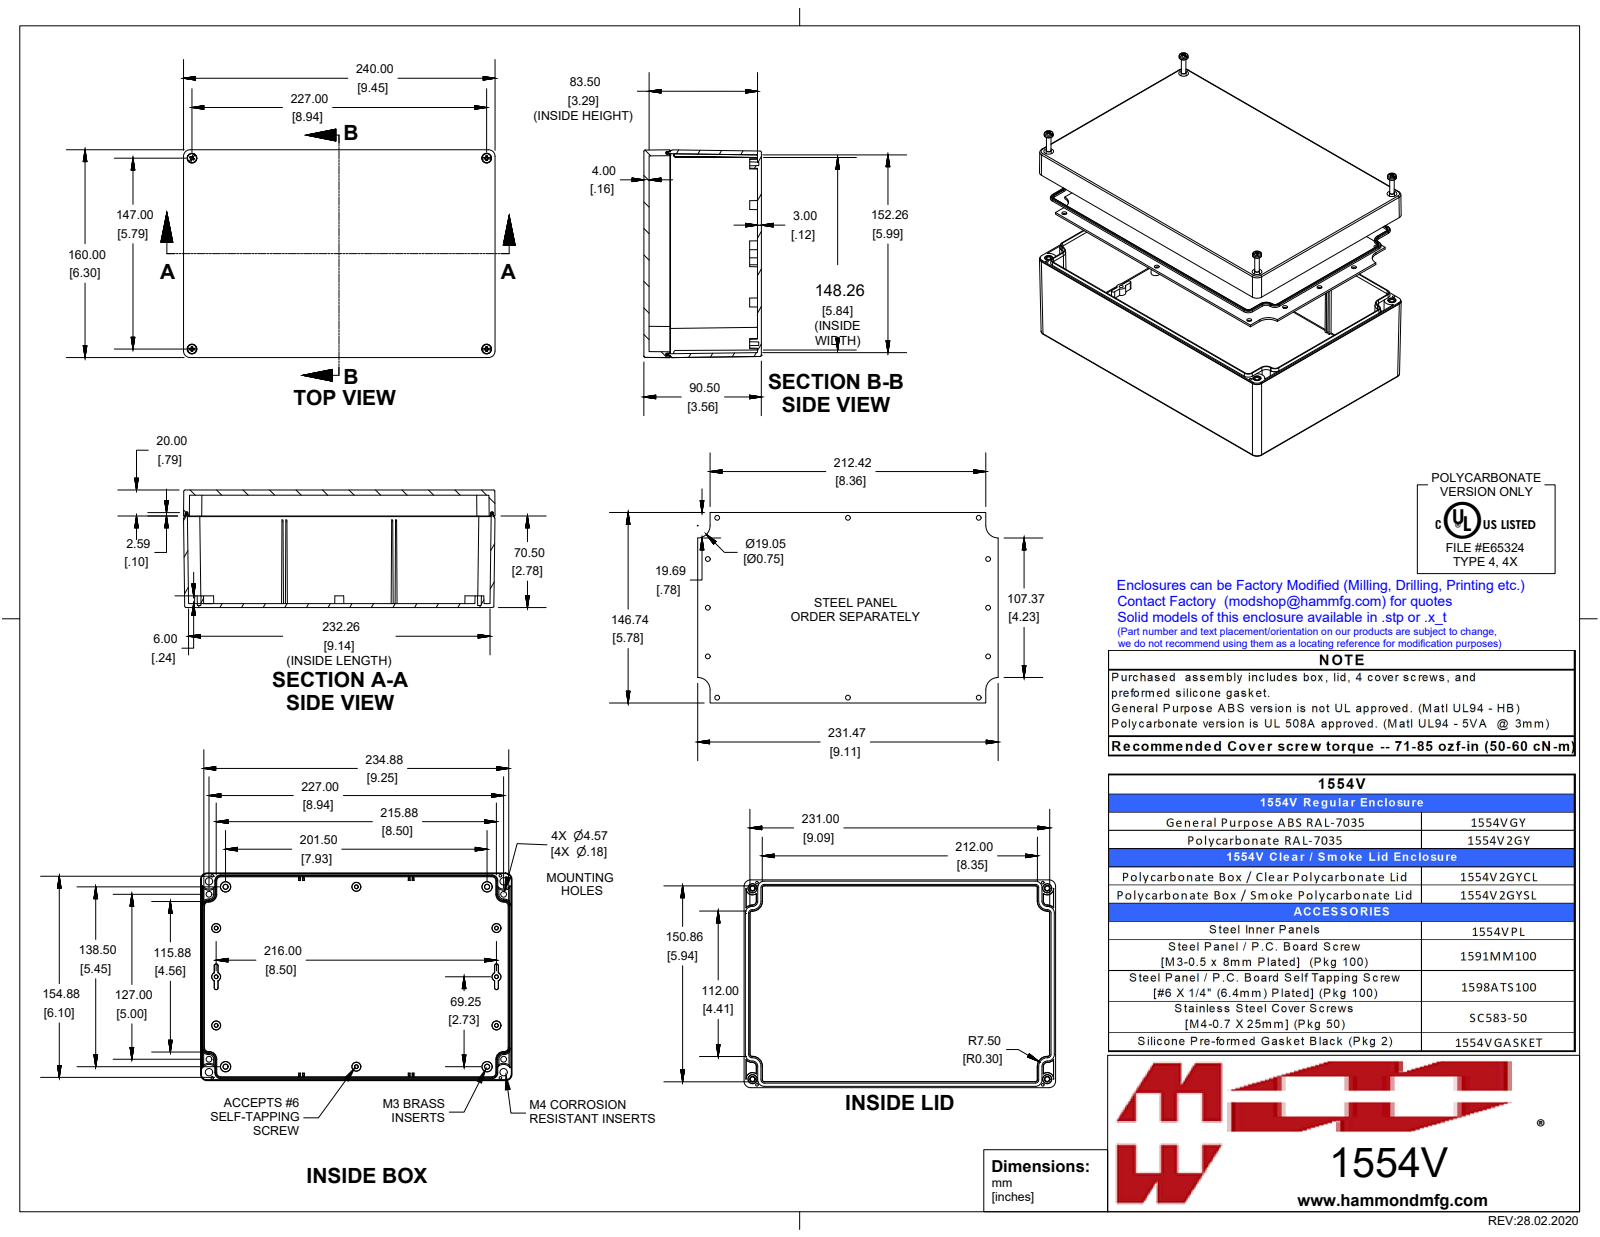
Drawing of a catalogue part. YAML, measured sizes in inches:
part_name: "1554V2GY"
step_written_by: "SolidWorks 2019 (AUTOMOTIVE_DESIGN)"
units: inches
bodies: {solids: 15, faces: 1354, planar: 402, cylindrical: 318, other: 634}
overall_size: [9.449, 6.299, 3.543]
volume: 30.91
surface_area: 503.1
round_holes:
  - {diameter: 0.079, count: 8}
  - {diameter: 0.097, count: 4}
  - {diameter: 0.128, count: 4}
  - {diameter: 0.138, count: 4}
round_bosses_or_shafts:
  - {diameter: 0.272, count: 4}
  - {diameter: 0.25, count: 4}
  - {diameter: 0.218, count: 4}
  - {diameter: 0.21, count: 4}
  - {diameter: 0.19, count: 4}
  - {diameter: 0.154, count: 4}
  - {diameter: 0.152, count: 4}
  - {diameter: 0.15, count: 4}
partial_cylinders:
  - {radius: 0.02, count: 32}
  - {radius: 0.039, count: 8}
  - {radius: 0.197, count: 8}
  - {radius: 0.059, count: 2}
face_to_face_distances: [0.118, 3.543, 0.157, 3.268, 3.386, 3.425, 0.177, 0.059, 2.756, 0.492]
hole_center_spacings: [0.197, 0.526, 0.529, 5.643, 5.805, 5.959, 6.128, 6.129]
